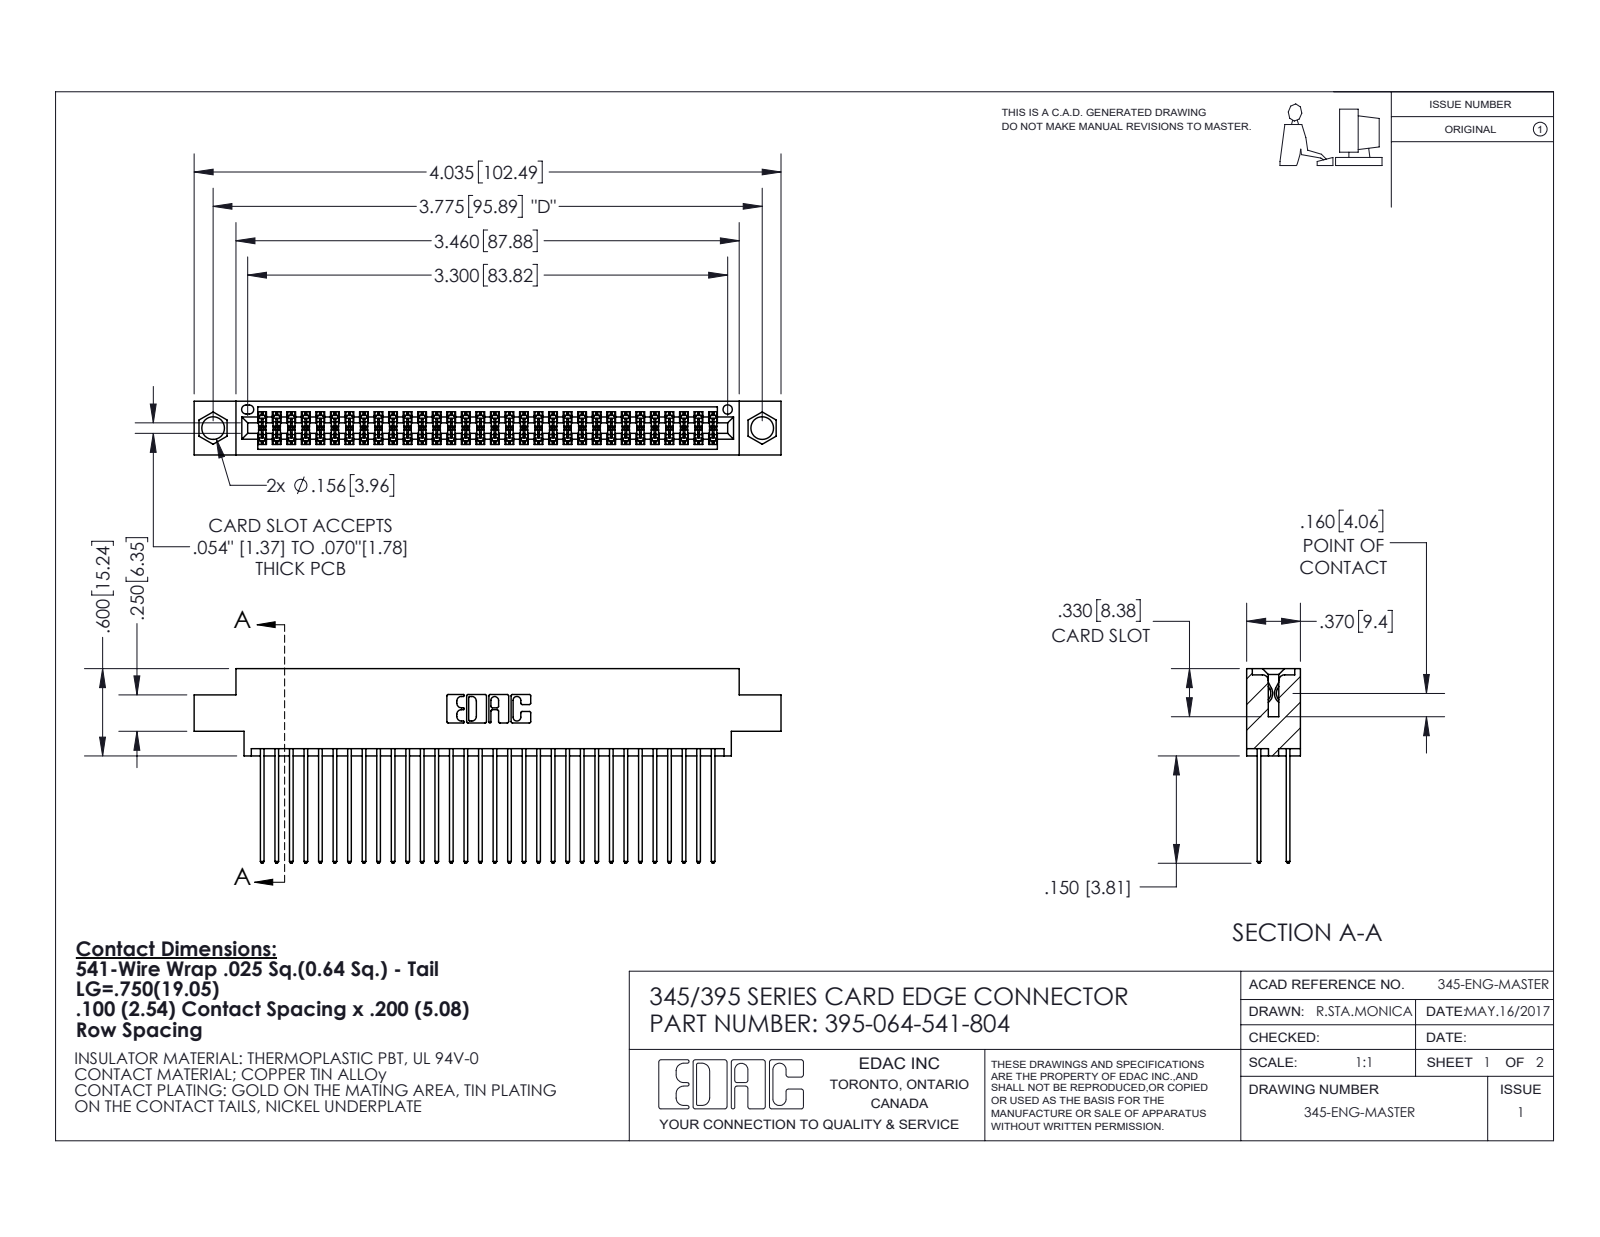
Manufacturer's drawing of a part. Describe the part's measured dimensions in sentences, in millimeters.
The part is named "345-292-001_345-293-141; 395-064-541-804; 345 Part_0.170 Offset - 0.156 Dia-TI". Its 3-D file was written by "SolidWorks 2020 (CONFIG_CONTROL_DESIGN)". It is 65 solids with 3344 faces: 2210 planar, 1134 cylindrical and 0 other. Overall it measures 102.5 by 34 by 9.4 millimeters. Its volume is 10 000 cubic millimeters and its surface area 16 320 square millimeters. Round holes: 2 of diameter 4, 1 of diameter 1.6. Partial cylindrical surfaces (rounded edges, fillets, slot ends): 128 of radius 0.2, 64 of radius 0.3, 22 of radius 0.3, 6 of radius 0.2, 6 of radius 0.8, 3 of radius 0.7, 2 of radius 0.4, 2 of radius 0.5. The main face-to-face distances are 1.8, 7.6, 5.1, 2.5, 6.9, 0.6, 9.4, 5.7, 4.4, 3.8. The hole center spacings are 6.9, 89.9, 95.9.
